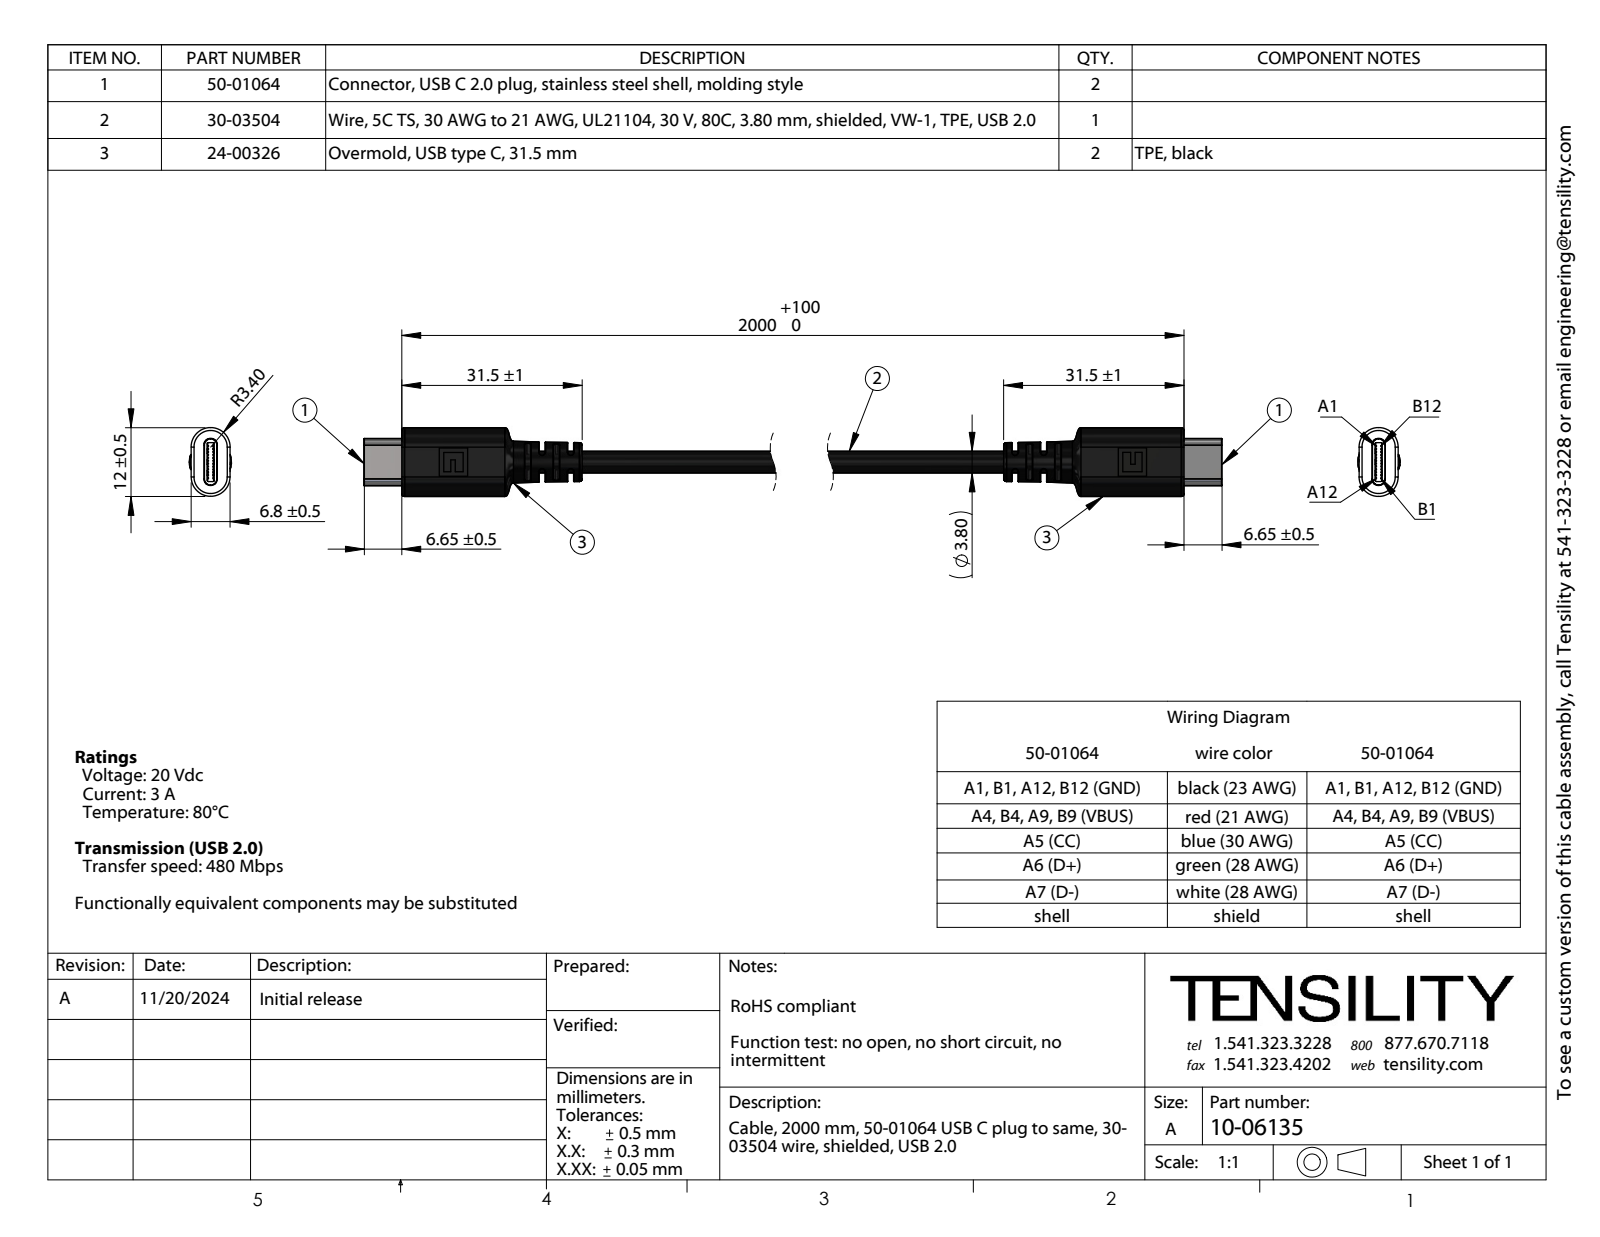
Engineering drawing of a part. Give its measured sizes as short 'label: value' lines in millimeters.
name: 10-06135; 30-03504_wbc; 24-00326; 50-01064_Hidden emarker
written by: SolidWorks 2021 (CONFIG_CONTROL_DESIGN)
unit: mm
bodies: 5 solids, 744 faces (382 planar, 134 cylindrical, 228 other)
size: 202.3 × 12 × 7.38
volume: 4 408 mm³; area: 6 275 mm²
holes: 1× ⌀2.98
bosses: 1× ⌀3.8
rounds: 20× R0.5, 4× R0.1, 4× R0.15, 4× R0.25, 2× R0.6, 2× R1.18, 2× R3.4
face distances: 6.8, 2.5, 2.35, 2.23, 4.57, 4.58, 2.22, 0.65, 1.7, 1
